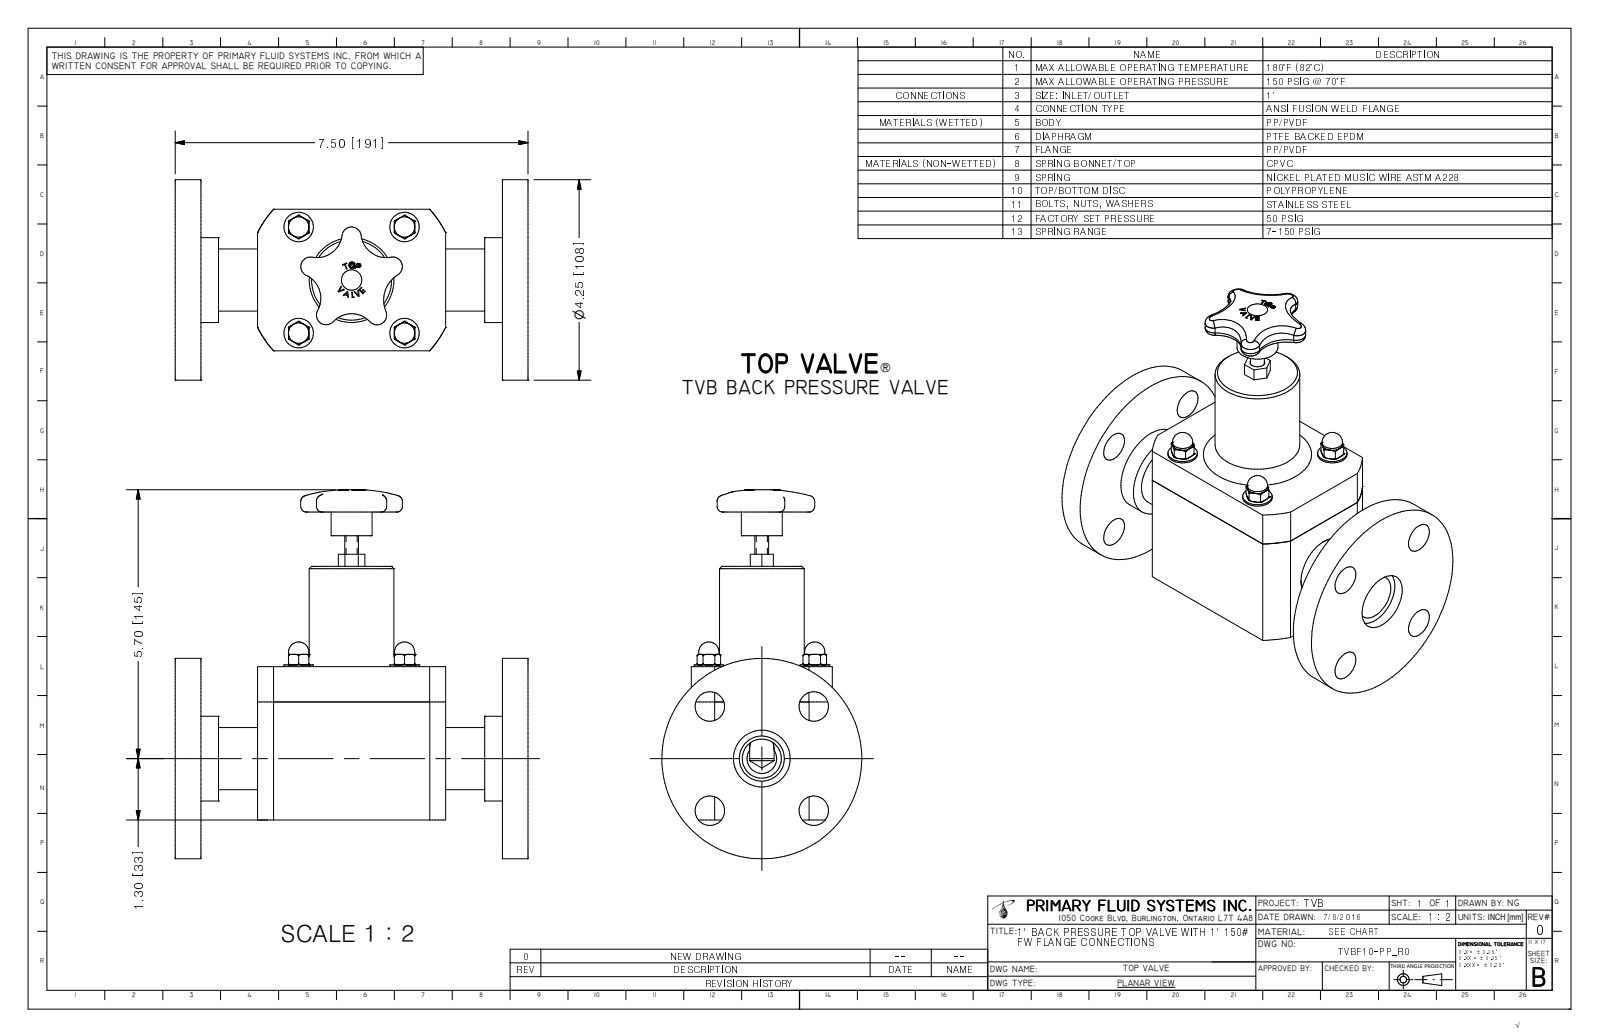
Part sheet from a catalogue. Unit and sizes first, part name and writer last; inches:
Units: inches
Overall size (bounding box): 7.827 × 7.5 × 4.25
Round holes (diameter × count): ⌀0.175 ×4, ⌀0.625 ×4, ⌀0.957 ×1, ⌀1.205 ×1
Round bosses / shafts (diameter × count): ⌀0.625 ×4, ⌀0.433 ×4, ⌀0.375 ×4, ⌀1.8 ×2, ⌀4.25 ×1, ⌀1.315 ×1, ⌀0.87 ×1, ⌀0.293 ×1
Partial cylindrical surfaces — rounded edges, fillets, slot ends (radius × count): R0.085 ×5, R0.205 ×5, R0.536 ×4, R0.656 ×4, R0.625 ×1, R0.745 ×1, R2.238 ×1, R2.238 ×1
Main face-to-face distances: 0.545, 6.955, 7.5, 3, 6.41, 1.75, 5.75, 1.205, 5.205, 3.25
Hole centre spacings: 1.562, 2.209, 2.25, 3.125, 3.182
Volume: 59.38 in³ · Surface area: 190.1 in²
Bodies: 1 solid, 369 faces (156 planar, 65 cylindrical, 148 other)
Part name (STEP PRODUCT): TVBF10-PP_R0
STEP written by: Autodesk Inventor 2009 (AUTOMOTIVE_DESIGN)
